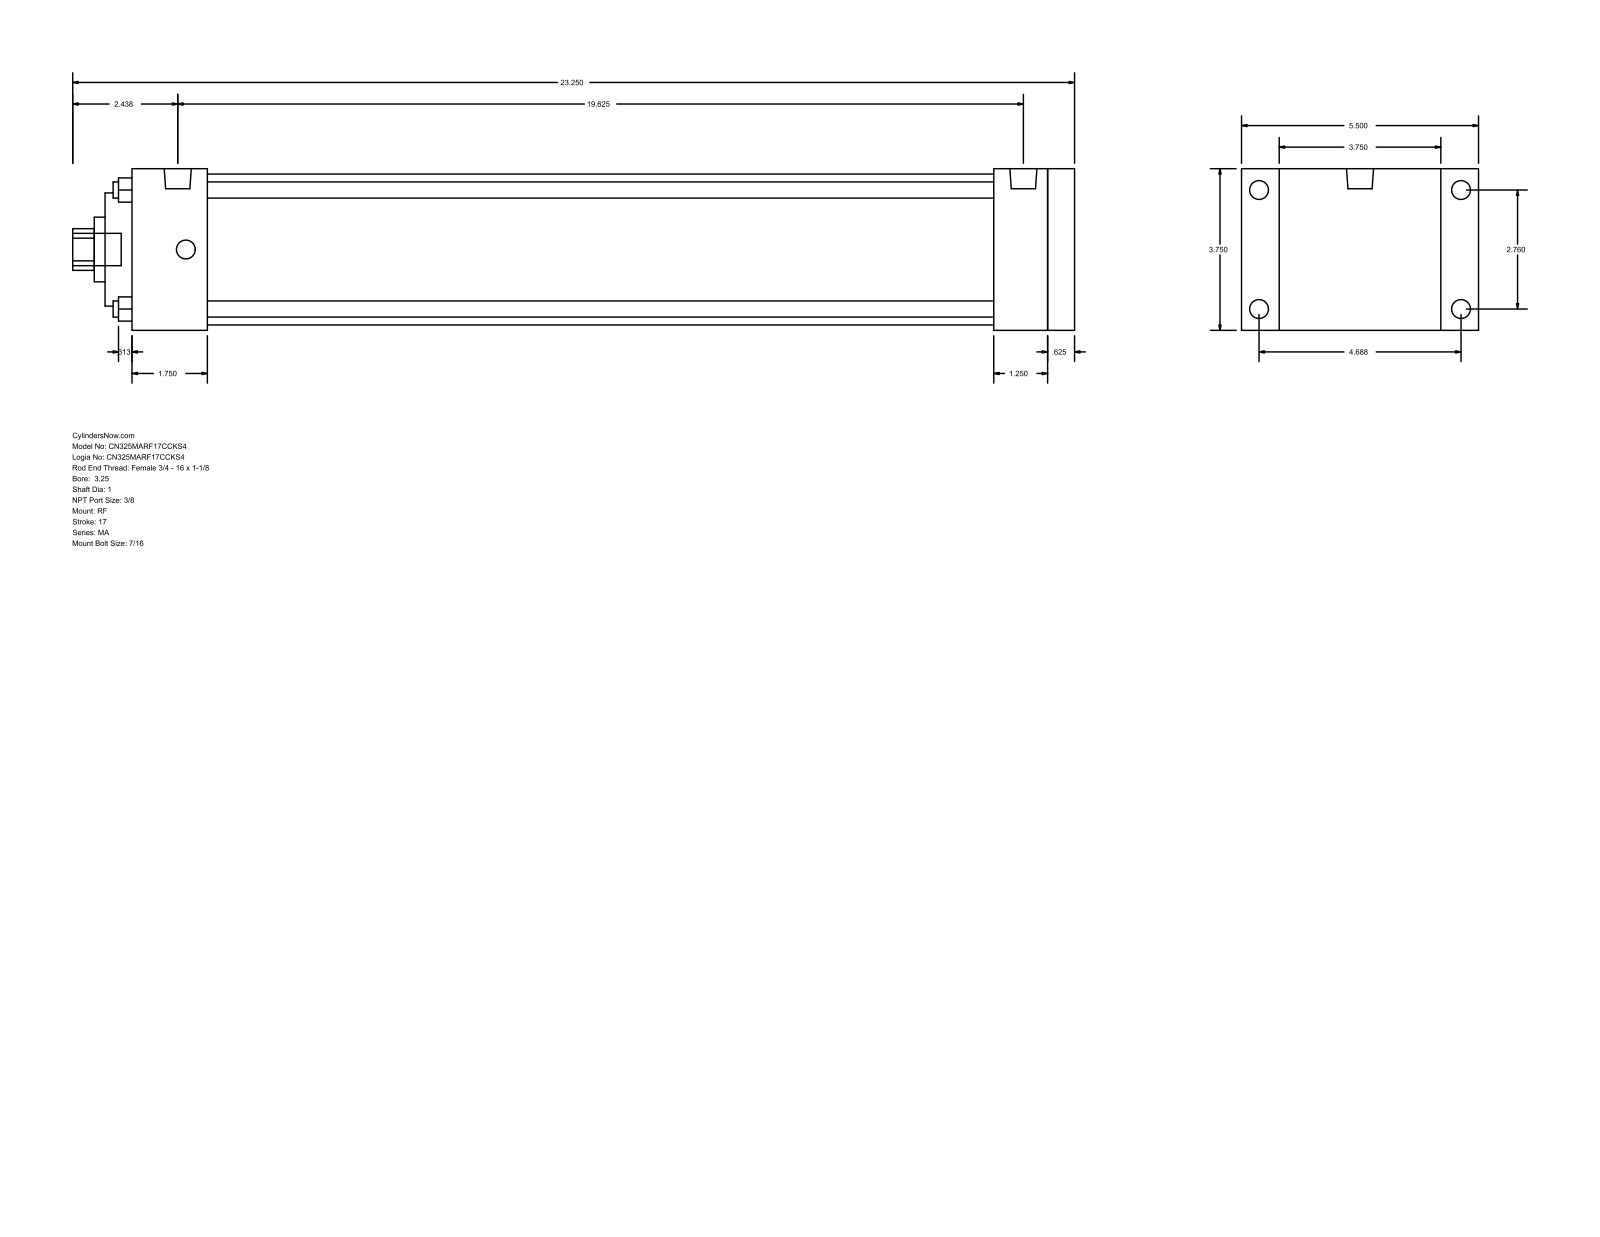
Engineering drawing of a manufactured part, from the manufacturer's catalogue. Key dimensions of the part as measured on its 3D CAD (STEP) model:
Part name (STEP PRODUCT): MA_RF__0325_1
STEP written by: GSSL Pune (CONFIG_CONTROL_DESIGN)
Units: millimetres
Bodies: 0 solids, 94 faces (65 planar, 29 cylindrical, 0 other)
Overall size (bounding box): 590.55 × 139.7 × 95.25
Round holes (diameter × count): ⌀9.53 ×4, ⌀25.4 ×1, ⌀38.1 ×1, ⌀66.67 ×1, ⌀88.9 ×1
Round bosses / shafts (diameter × count): ⌀11.11 ×8, ⌀15.93 ×2, ⌀19.05 ×1
Partial cylindrical surfaces — rounded edges, fillets, slot ends (radius × count): R12.29 ×1
Main face-to-face distances: 95.24, 555.63, 539.75, 15.88, 22.23, 117.47, 15.87, 508, 31.75, 47.63
Hole centre spacings: 49.57, 70.1, 99.14
